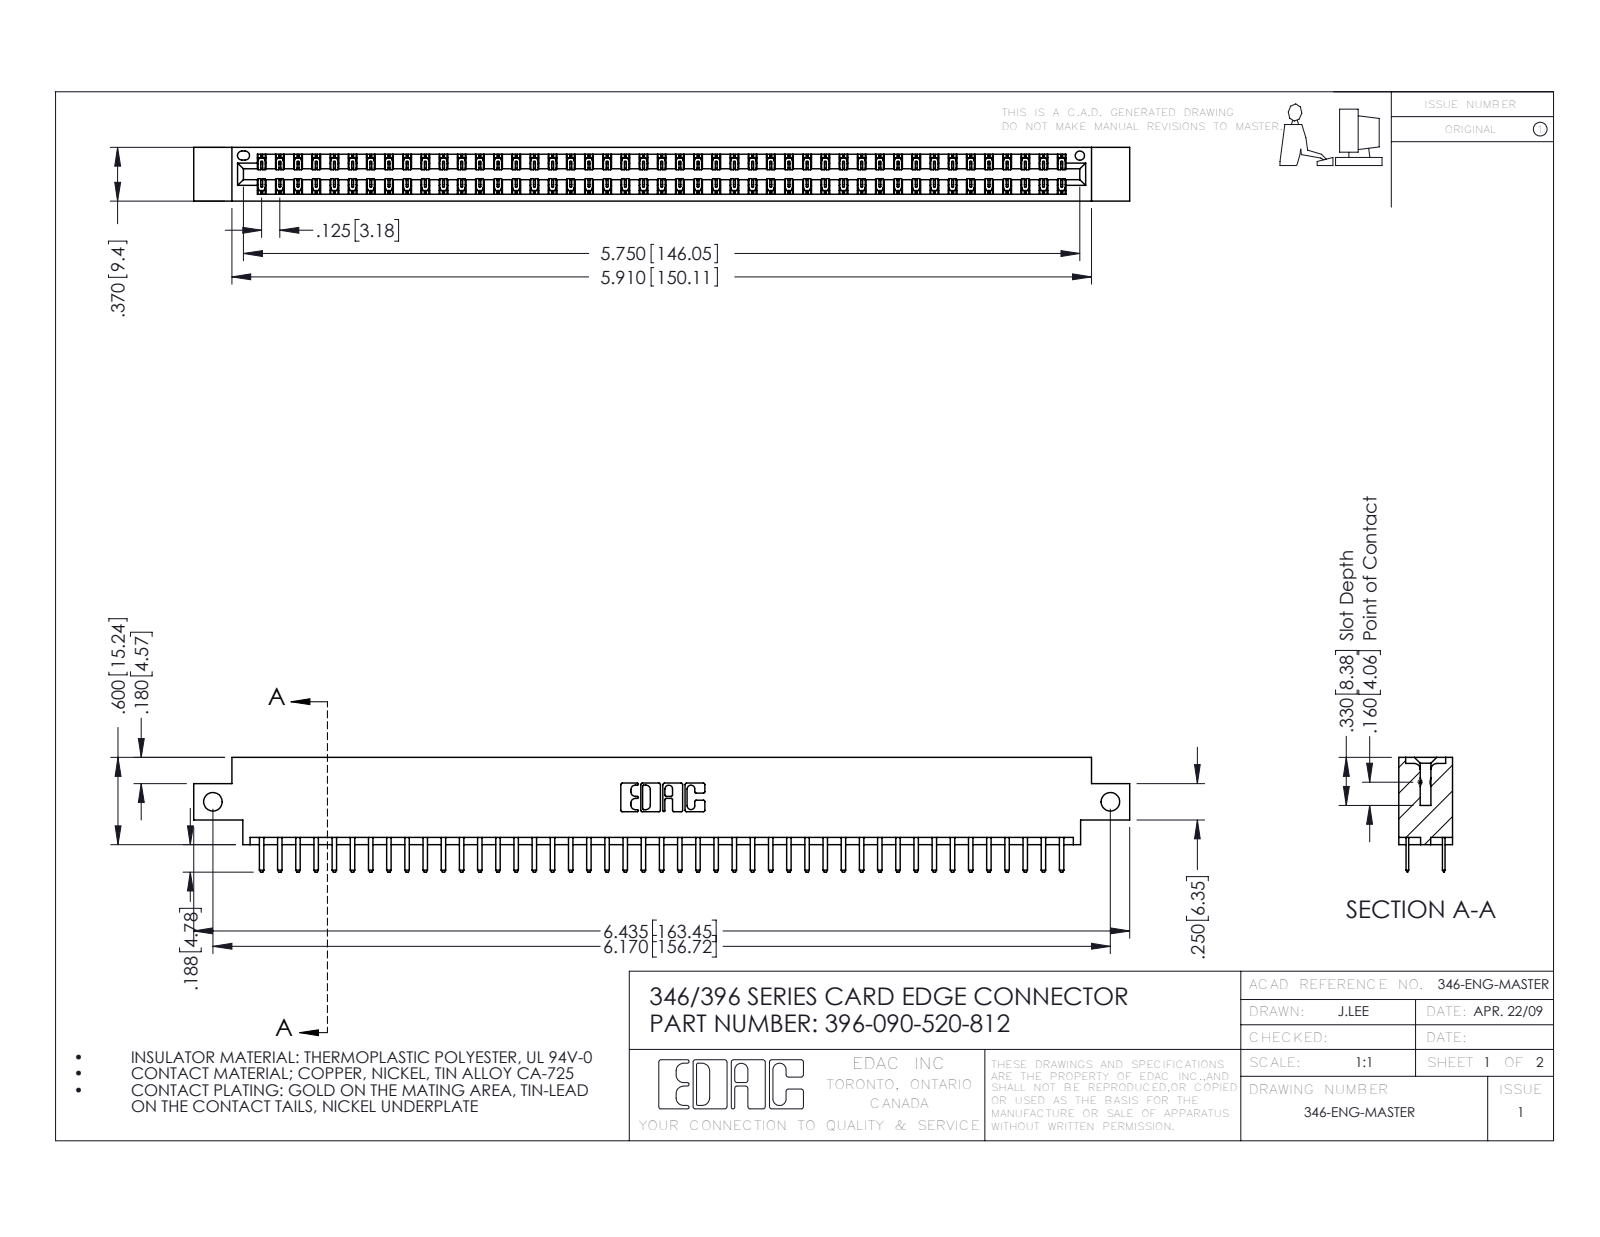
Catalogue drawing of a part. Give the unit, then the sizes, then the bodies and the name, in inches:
Units: inches
Overall size (bounding box): 6.435 × 0.788 × 0.37
Round holes (diameter × count): ⌀0.128 ×2, ⌀0.064 ×1
Partial cylindrical surfaces — rounded edges, fillets, slot ends (radius × count): R0.006 ×135, R0.01 ×94, R0.01 ×22, R0.007 ×6, R0.031 ×6, R0.026 ×3, R0.014 ×2, R0.022 ×2
Main face-to-face distances: 0.048, 0.322, 0.25, 0.37, 0.275, 0.072, 0.298, 0.025, 0.148, 0.222
Hole centre spacings: 6.17
Volume: 0.957 in³ · Surface area: 33.4 in²
Bodies: 91 solids, 5166 faces (3410 planar, 1756 cylindrical, 0 other)
Part name (STEP PRODUCT): 346 Part_0.170 Offset - Side Mount; 345-292-001_345-293-120; 396-090-520-812
STEP written by: SolidWorks 2016 (CONFIG_CONTROL_DESIGN)
